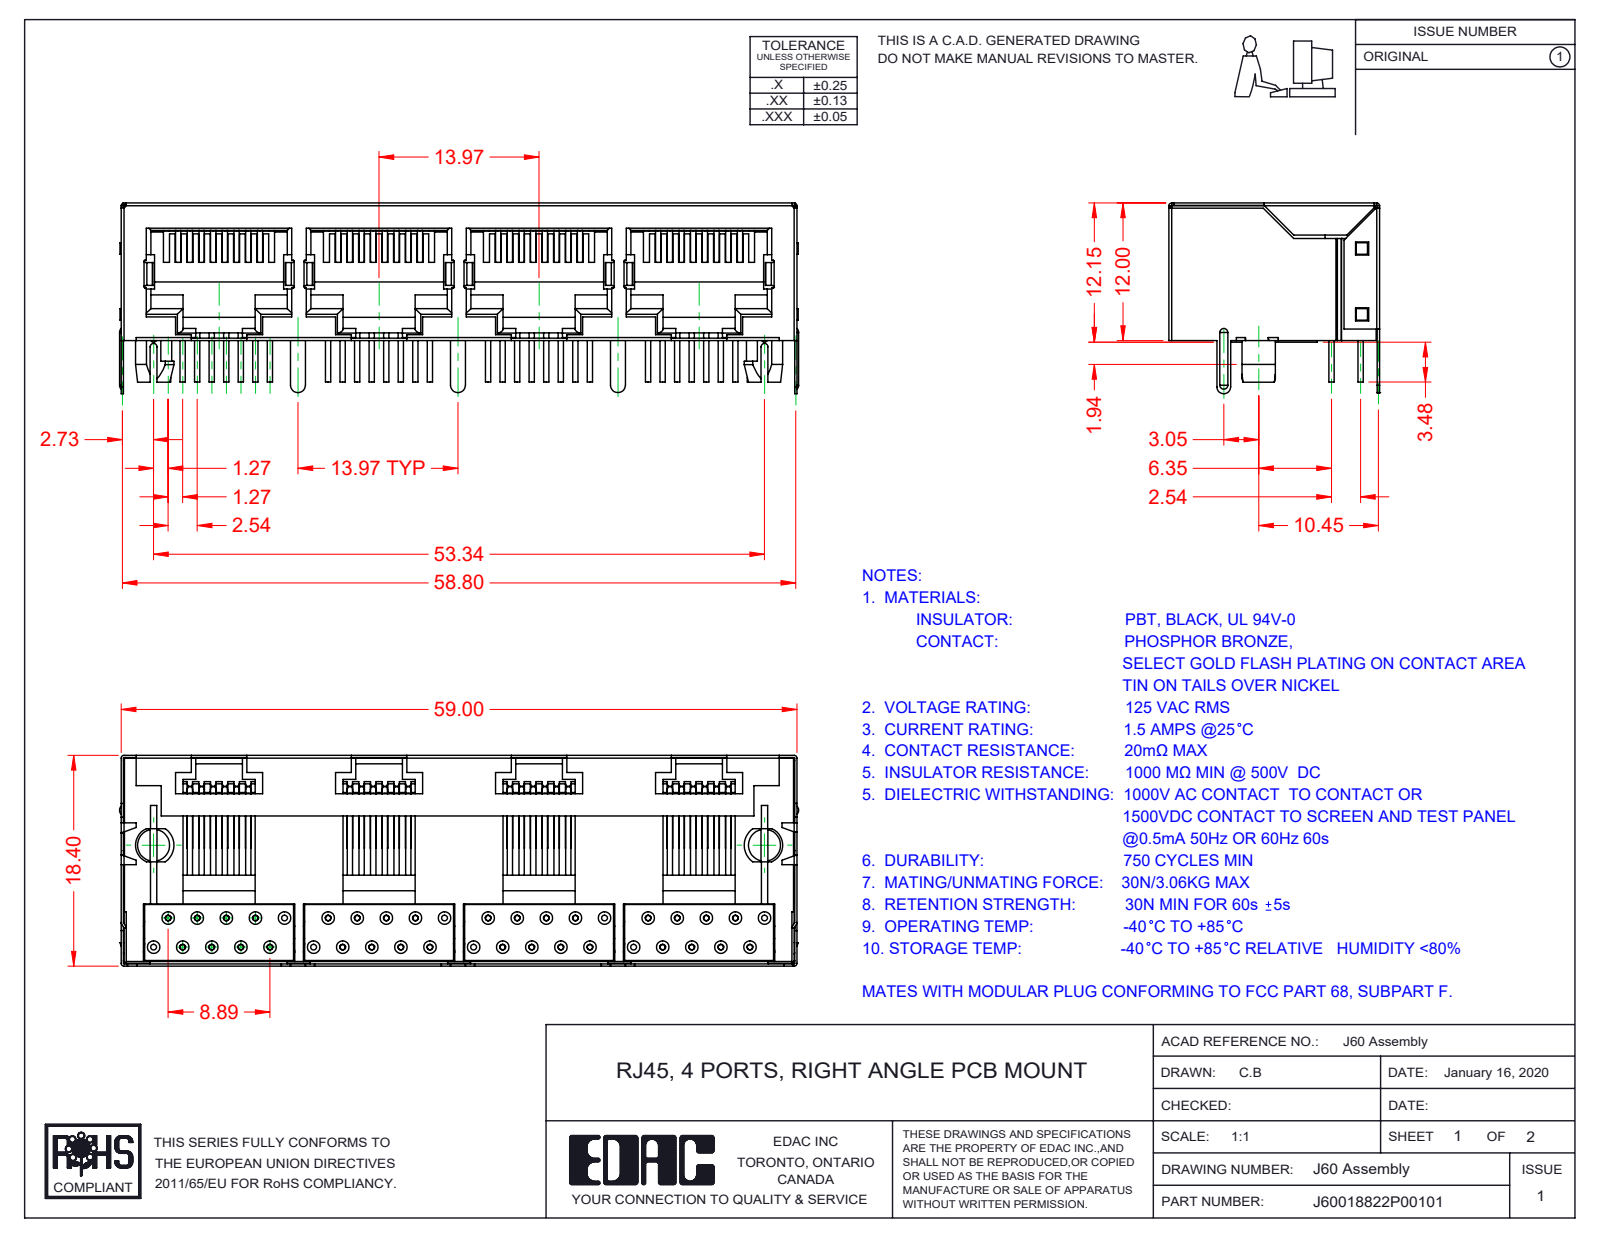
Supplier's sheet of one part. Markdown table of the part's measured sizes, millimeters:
| quantity | value |
| --- | --- |
| part name | 60 Shield; RJ60048822P00101; 60 Contacts_8P8C; 60 Insulator |
| STEP written by | SolidWorks 2016 (CONFIG_CONTROL_DESIGN) |
| units | millimeters |
| bodies | 34 solids, 2562 faces (1489 planar, 715 cylindrical, 358 other) |
| overall size | 59.3 × 18.4 × 16.65 |
| volume | 7 013 mm³ |
| surface area | 18 560 mm² |
| round holes (diameter × count) | 0.5 × 40, 1.1 × 40 |
| round bosses / shafts (diameter × count) | 0.46 × 96 |
| partial cylindrical surfaces (radius × count) | 0.3 × 26, 0.25 × 21, 0.5 × 18, 0.1 × 16, 0.21 × 10, 0.8 × 7, 0.65 × 3, 0.28 × 2 |
| main face-to-face distances | 0.5, 11.75, 11.55, 13.97, 2.19, 5.38, 5.18, 4.88, 18.2, 11.5 |
| hole center spacings | 2.84, 2.54, 4.58, 13.97, 5.08, 12.95, 15.45, 11.43 |
